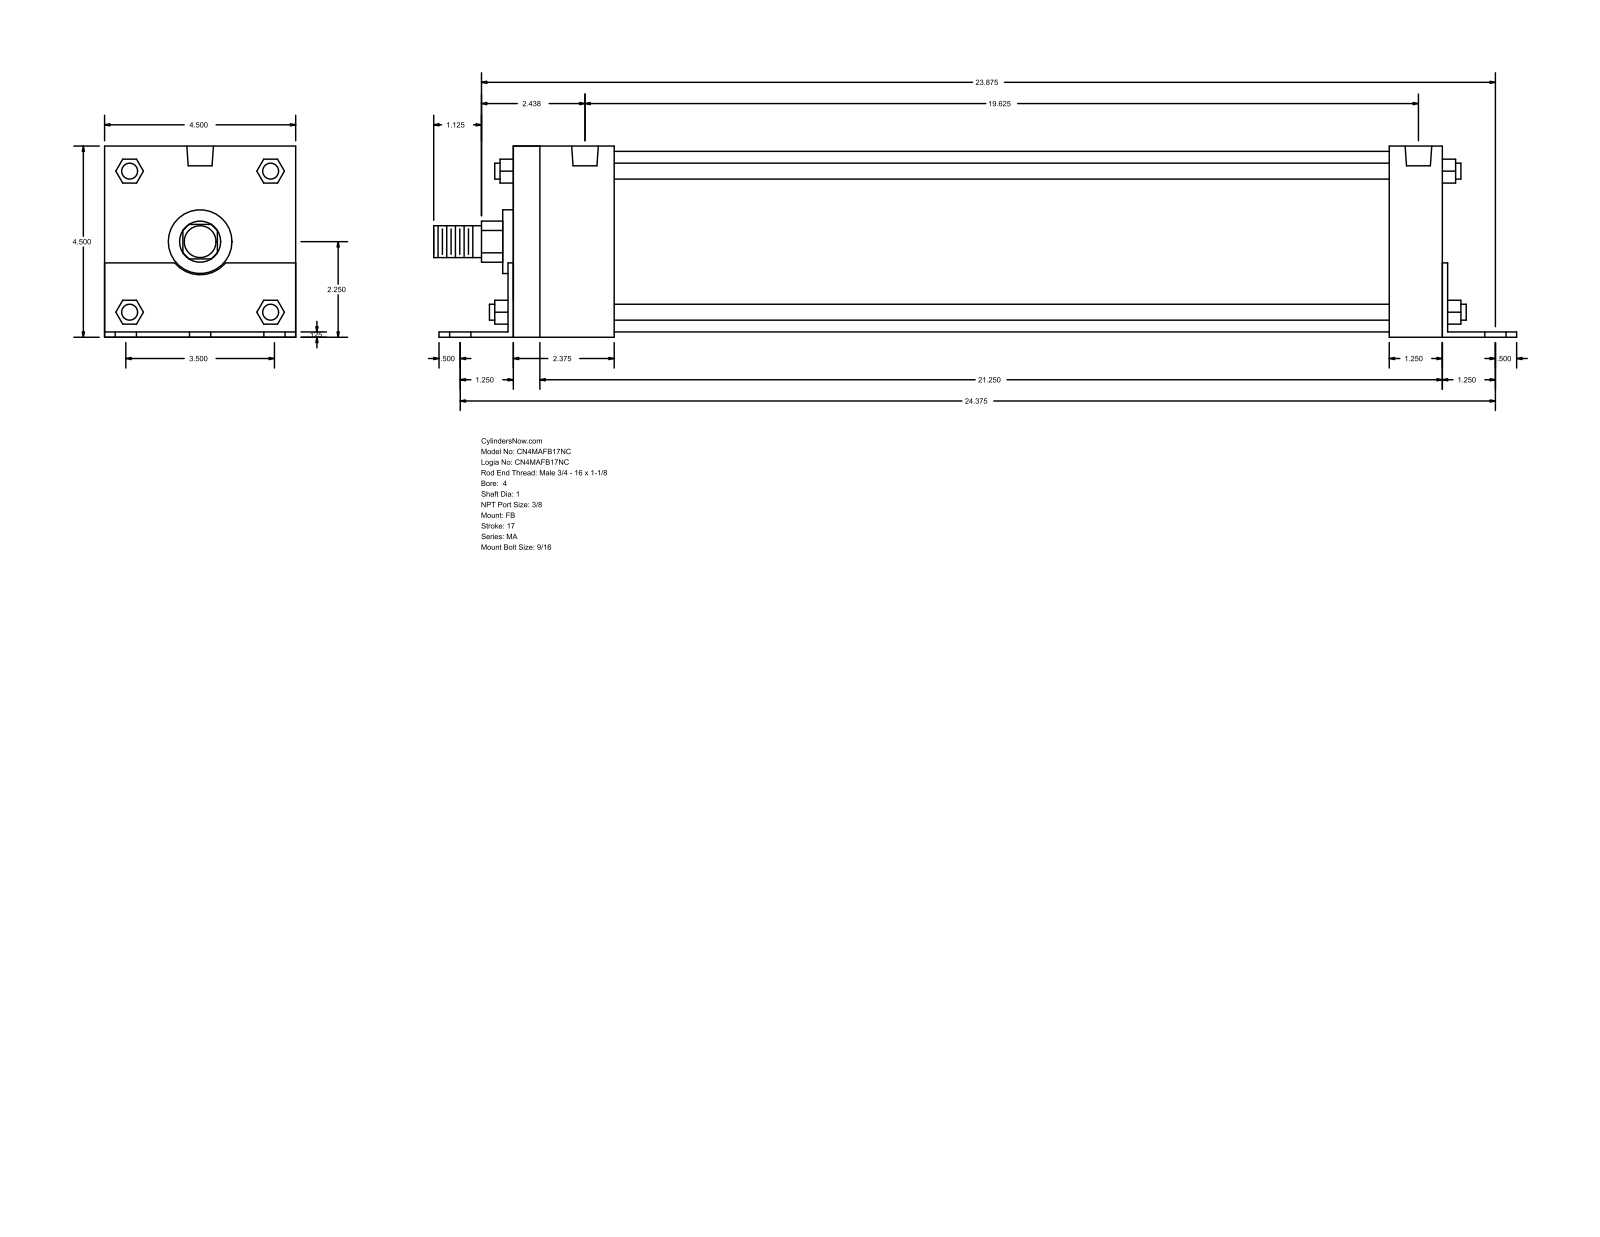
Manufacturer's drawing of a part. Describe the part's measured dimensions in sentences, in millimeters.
The part is named "MA_FB__0400_1". Its 3-D file was written by "GSSL Pune (CONFIG_CONTROL_DESIGN)". It is 0 solids with 140 faces: 105 planar, 35 cylindrical and 0 other. Overall it measures 647.7 by 114.35 by 114.3 millimeters. Round holes: 6 of diameter 14.29, 4 of diameter 11.11, 2 of diameter 15.93. Round bosses or shafts: 4 of diameter 9.53, 1 of diameter 107.95, 1 of diameter 38.1, 1 of diameter 25.4, 1 of diameter 19.05. Partial cylindrical surfaces (rounded edges, fillets, slot ends): 1 of radius 12.29, 1 of radius 19.81. The main face-to-face distances are 114.3, 3.17, 114.35, 3.12, 111.18, 555.62, 3.18, 561.97, 558.8, 558.79. The hole center spacings are 44.45, 620.71, 619.12, 63.99, 67.5, 86.85, 88.9, 90.97.
